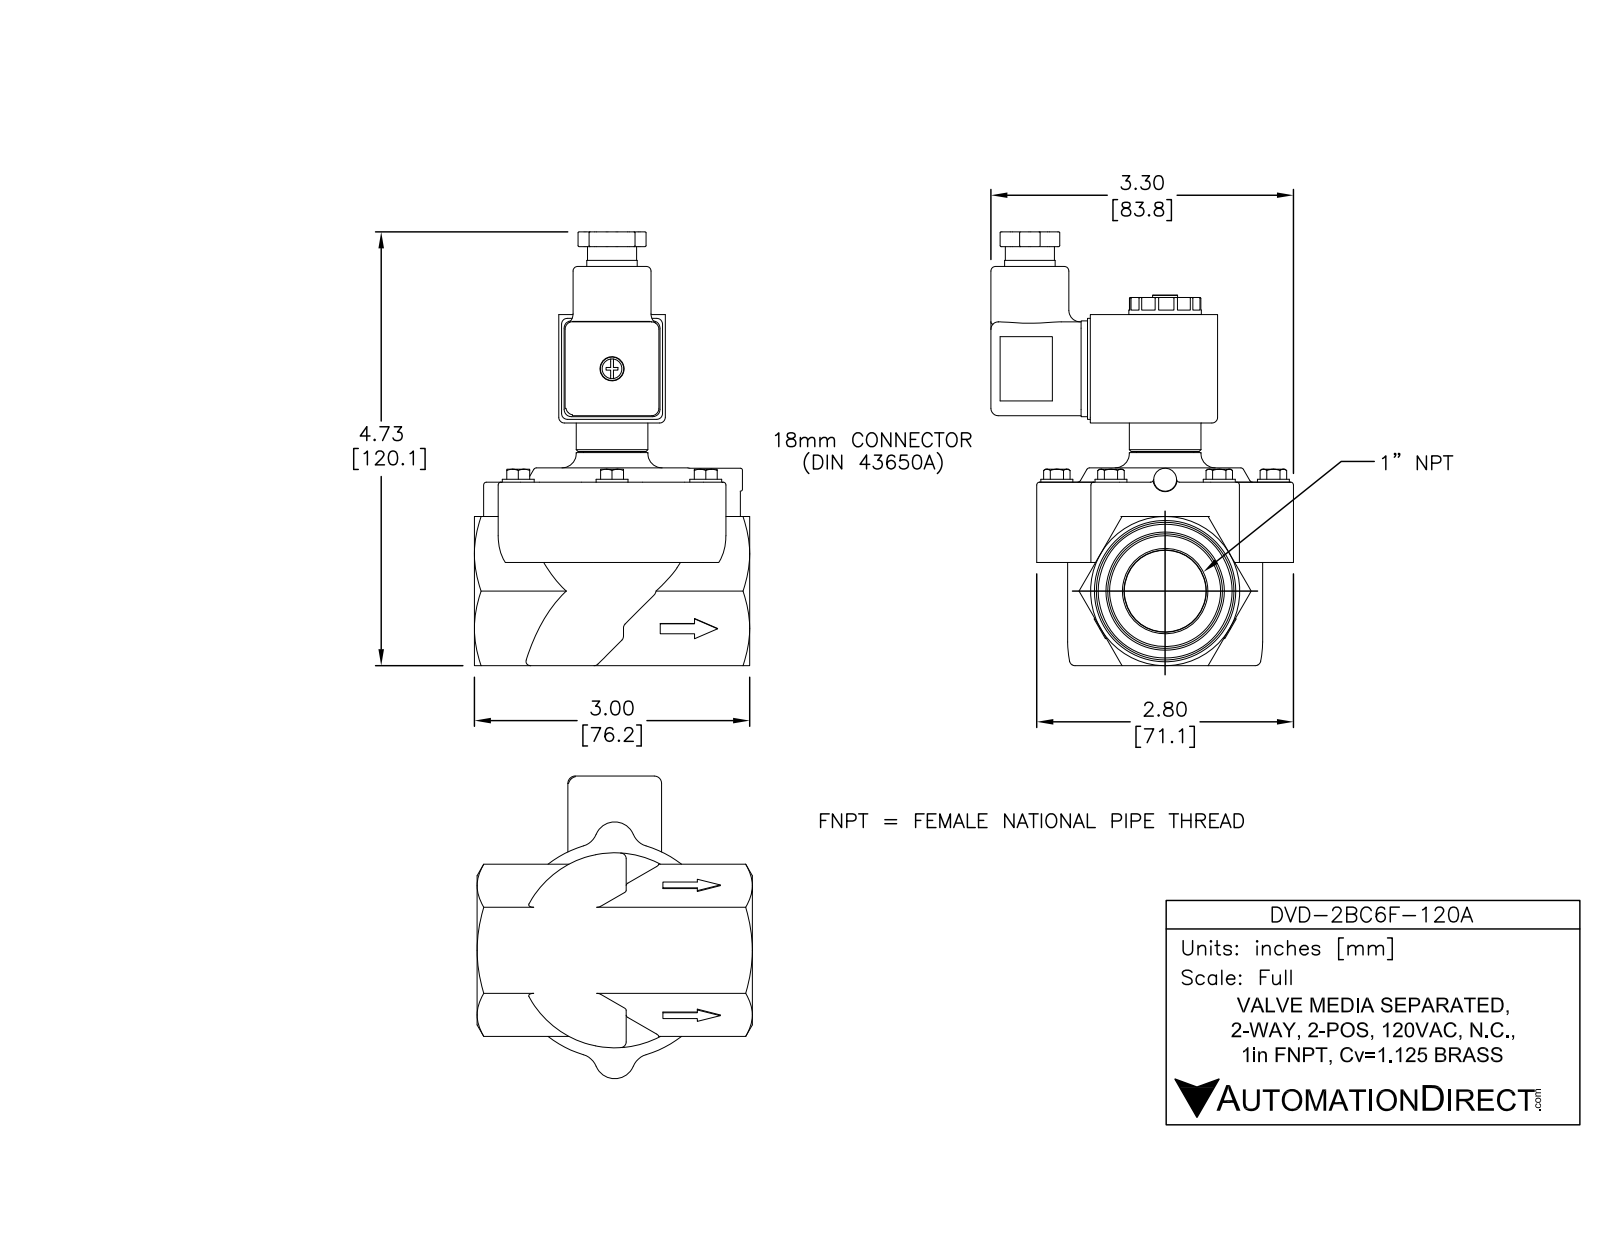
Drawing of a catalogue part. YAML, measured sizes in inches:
part_name: "DVD-2BC6F-120A"
step_written_by: "SolidWorks 2015 (AUTOMOTIVE_DESIGN)"
units: inches
bodies: {solids: 2, faces: 1898, planar: 894, cylindrical: 390, other: 614}
overall_size: [4.727, 3.298, 3]
volume: 8.288
surface_area: 101.4
round_holes:
  - {diameter: 0.2, count: 6}
  - {diameter: 0.236, count: 6}
  - {diameter: 0.185, count: 4}
  - {diameter: 0.06, count: 2}
  - {diameter: 0.125, count: 2}
  - {diameter: 0.156, count: 2}
  - {diameter: 0.185, count: 2}
  - {diameter: 1.125, count: 2}
  - {diameter: 0.047, count: 1}
  - {diameter: 0.065, count: 1}
  - {diameter: 0.067, count: 1}
  - {diameter: 0.078, count: 1}
round_bosses_or_shafts:
  - {diameter: 0.348, count: 6}
  - {diameter: 0.234, count: 6}
  - {diameter: 0.164, count: 6}
  - {diameter: 1.844, count: 1}
  - {diameter: 1.5, count: 1}
  - {diameter: 1.359, count: 1}
  - {diameter: 0.85, count: 1}
  - {diameter: 0.79, count: 1}
partial_cylinders:
  - {radius: 0.01, count: 48}
  - {radius: 0.219, count: 20}
  - {radius: 0.156, count: 16}
  - {radius: 0.062, count: 12}
  - {radius: 0.08, count: 12}
  - {radius: 0.03, count: 10}
  - {radius: 0.05, count: 8}
  - {radius: 0.031, count: 7}
face_to_face_distances: [1.609, 0.125, 1.629, 0.02, 1.625, 0.155, 0.048, 0.118, 1.043, 0.974]
hole_center_spacings: [1.18, 1.18, 2.044, 0.611, 1.669, 2.28, 1.103, 1.169]
